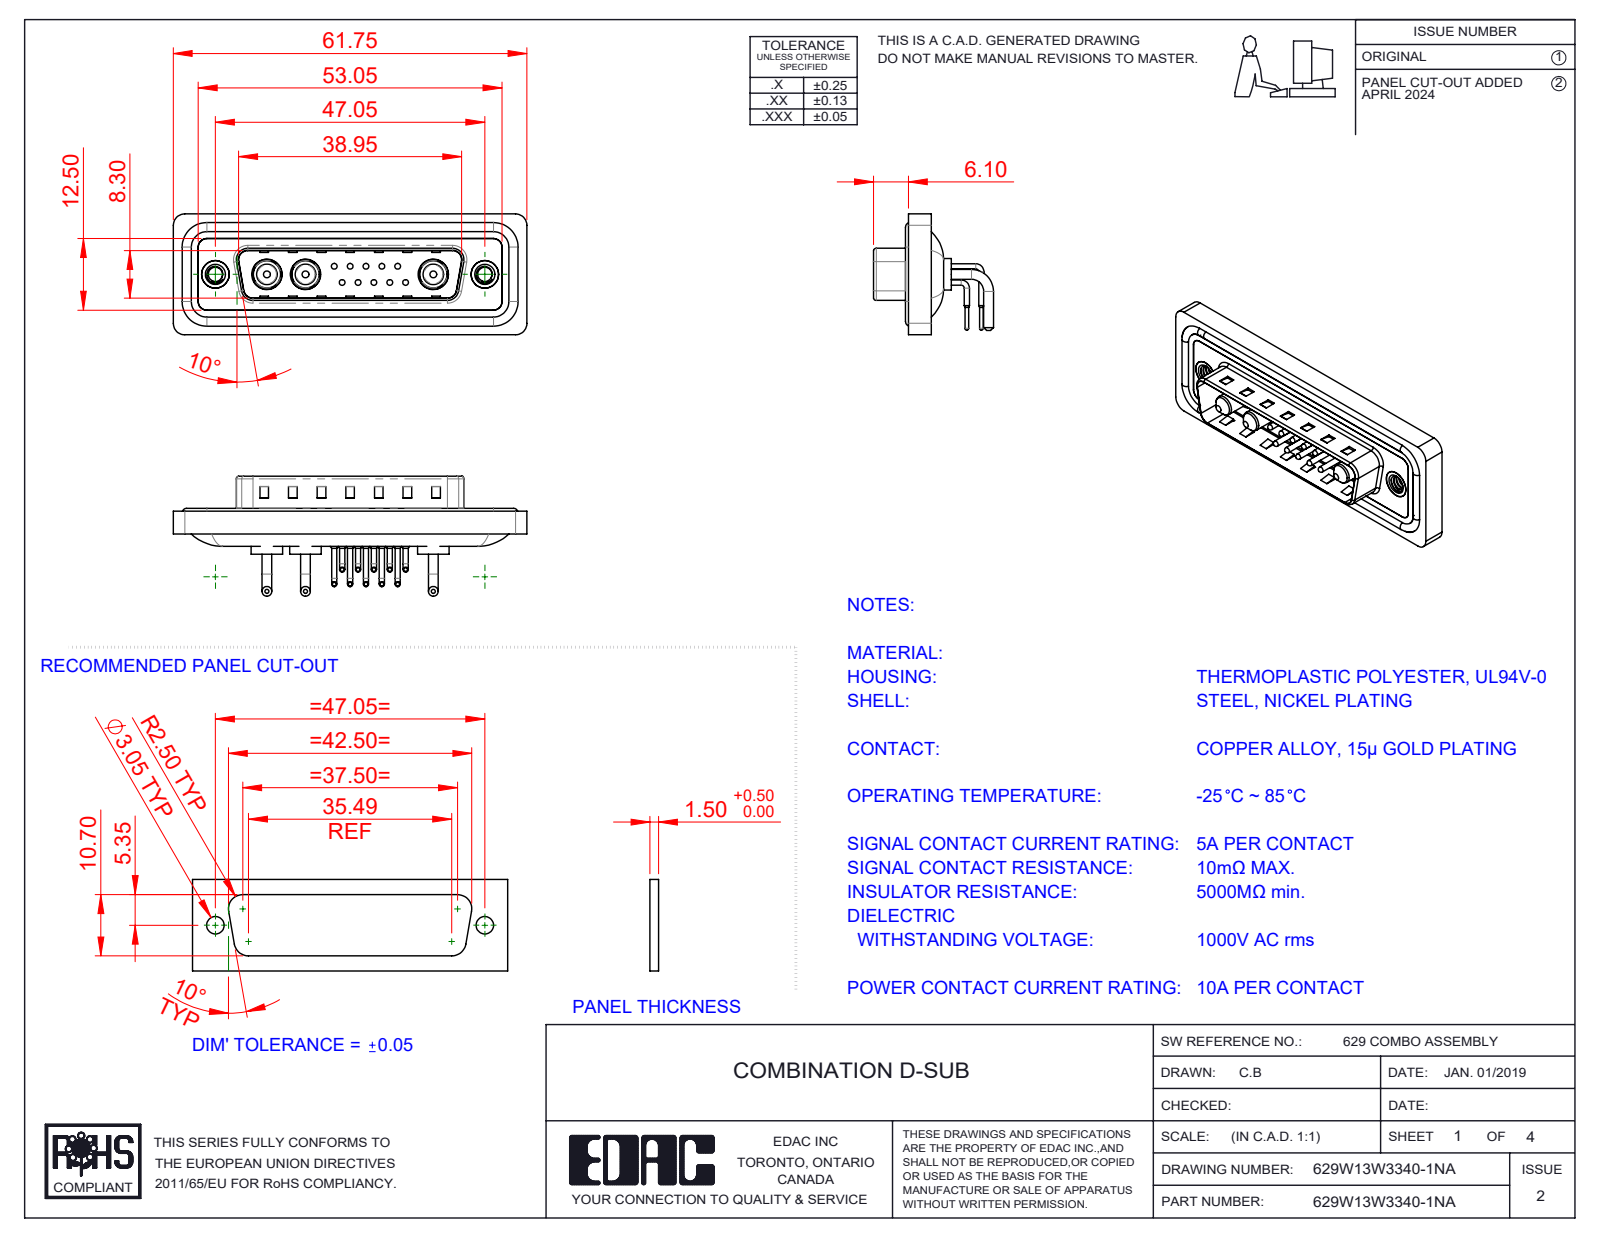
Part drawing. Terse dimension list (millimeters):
name: 629Combo Housing_13W3; 629Combo Waterproof Housing_25 Contacts; 629Combo Threaded Rivet_A; 629W13W3340-1NA (+5 more)
written by: SolidWorks 2023 (CONFIG_CONTROL_DESIGN)
unit: mm
bodies: 23 solids, 1706 faces (879 planar, 609 cylindrical, 218 other)
size: 61.75 × 21.1 × 20.95
volume: 7 440 mm³; area: 12 347 mm²
holes: 10× ⌀0.75, 10× ⌀1.6, 10× ⌀2, 3× ⌀4.85, 3× ⌀5.3, 2× ⌀2.5, 2× ⌀4, 2× ⌀4.8, 2× ⌀5
bosses: 20× ⌀0.9, 10× ⌀1.5, 10× ⌀1, 10× ⌀0.65, 6× ⌀1.7, 4× ⌀1.6, 3× ⌀5.5, 3× ⌀5.2
rounds: 18× R1.5, 18× R2, 10× R1.01, 8× R0.5, 8× R1.6, 4× R0.25, 4× R0.6, 4× R0.65
face distances: 0.4, 2.9, 0.8, 4.1, 1.1, 2.1, 1.6, 4.5, 1.5, 6
hole spacings: 3.16, 2.77, 5.04, 5.54, 7.49, 5.03, 8.31, 10.11
